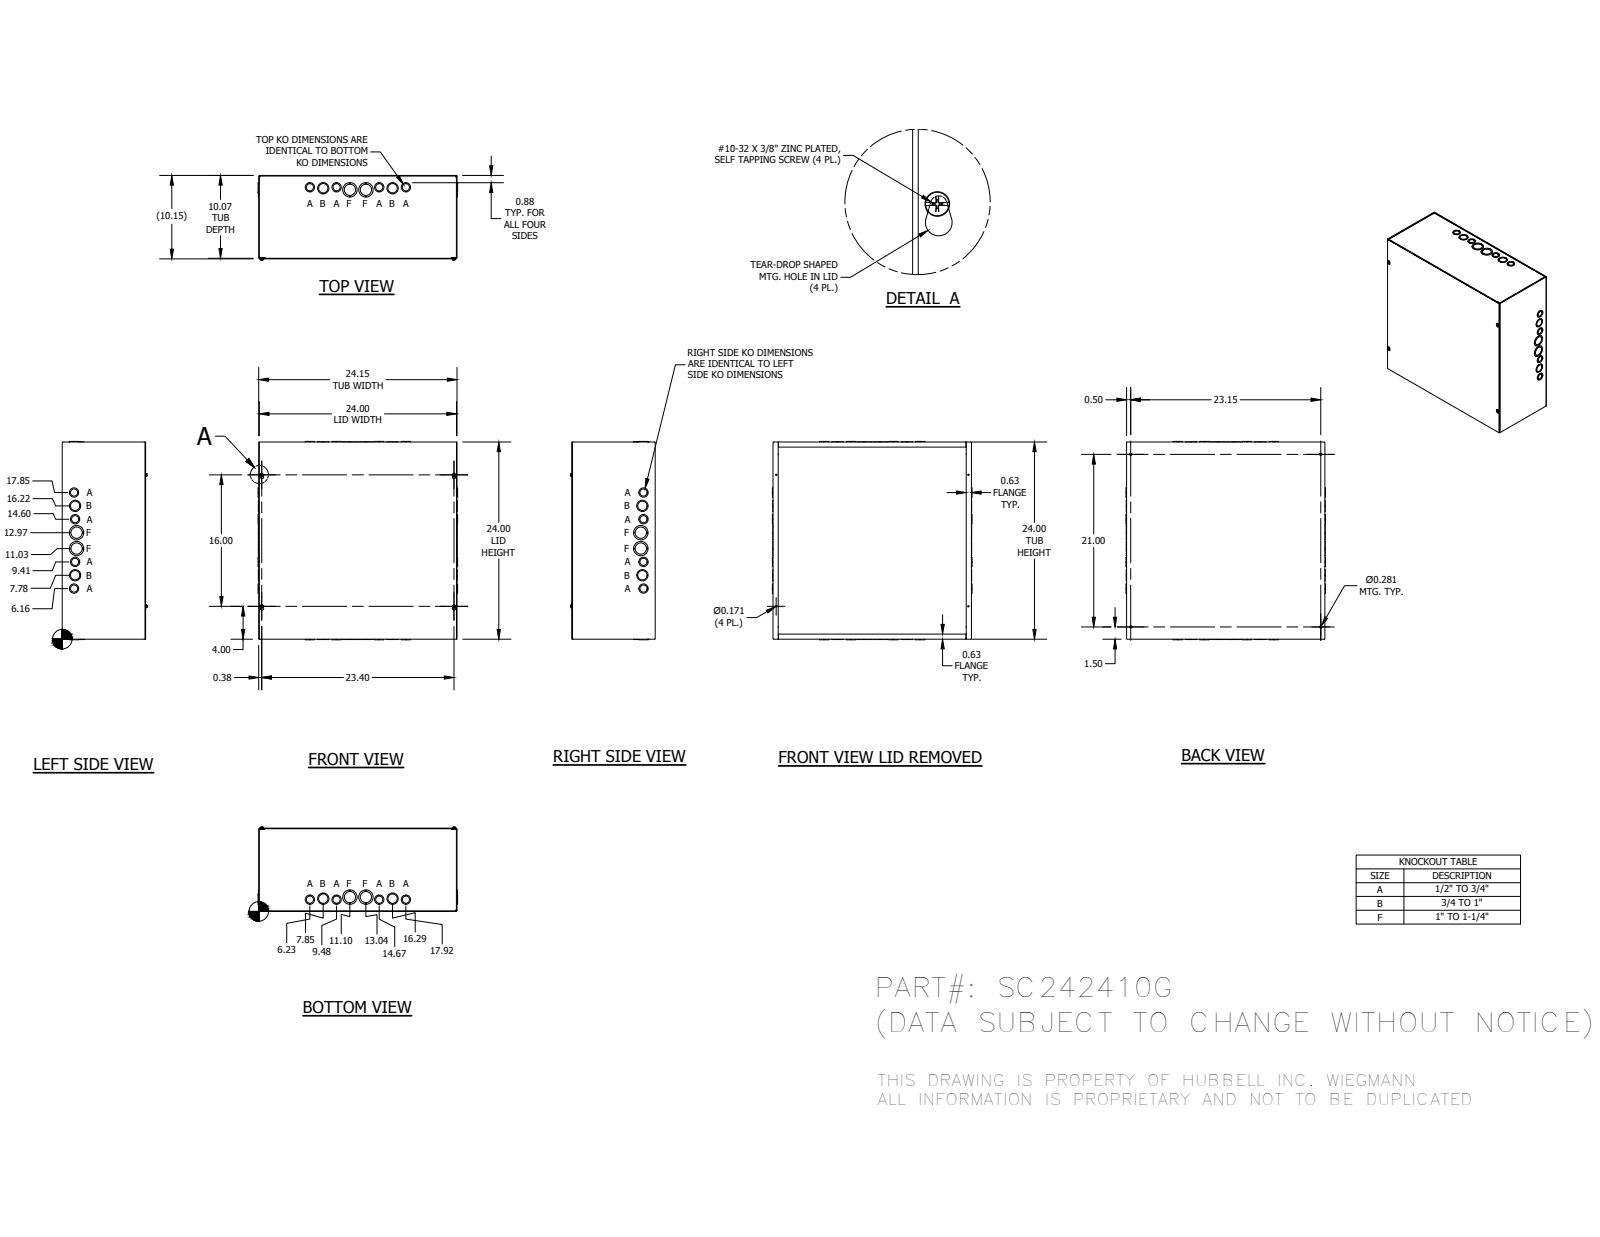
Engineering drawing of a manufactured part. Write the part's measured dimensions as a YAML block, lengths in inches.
part_name: "SC242410GBLR; SC2410GTB; SC2424GLPA; 37214 (+1 more)"
step_written_by: "Autodesk Inventor 2014 (AUTOMOTIVE_DESIGN)"
units: inches
bodies: {solids: 37, faces: 1219, planar: 899, cylindrical: 236, other: 84}
overall_size: [24.296, 24.148, 10.28]
round_holes:
  - {diameter: 1.125, count: 14}
  - {diameter: 0.875, count: 10}
  - {diameter: 1.375, count: 8}
  - {diameter: 0.171, count: 4}
  - {diameter: 0.281, count: 4}
  - {diameter: 1.75, count: 4}
round_bosses_or_shafts:
  - {diameter: 0.19, count: 4}
partial_cylinders:
  - {radius: 0.016, count: 12}
  - {radius: 0.09, count: 12}
  - {radius: 0.125, count: 4}
  - {radius: 0.203, count: 4}
face_to_face_distances: [0.074, 10.074, 10, 10.148, 24, 23.926, 24.074, 24.148, 23.852, 0.148]
hole_center_spacings: [1.63, 1.63, 1.655, 2.503, 3.25, 3.256, 3.579, 4.885]
